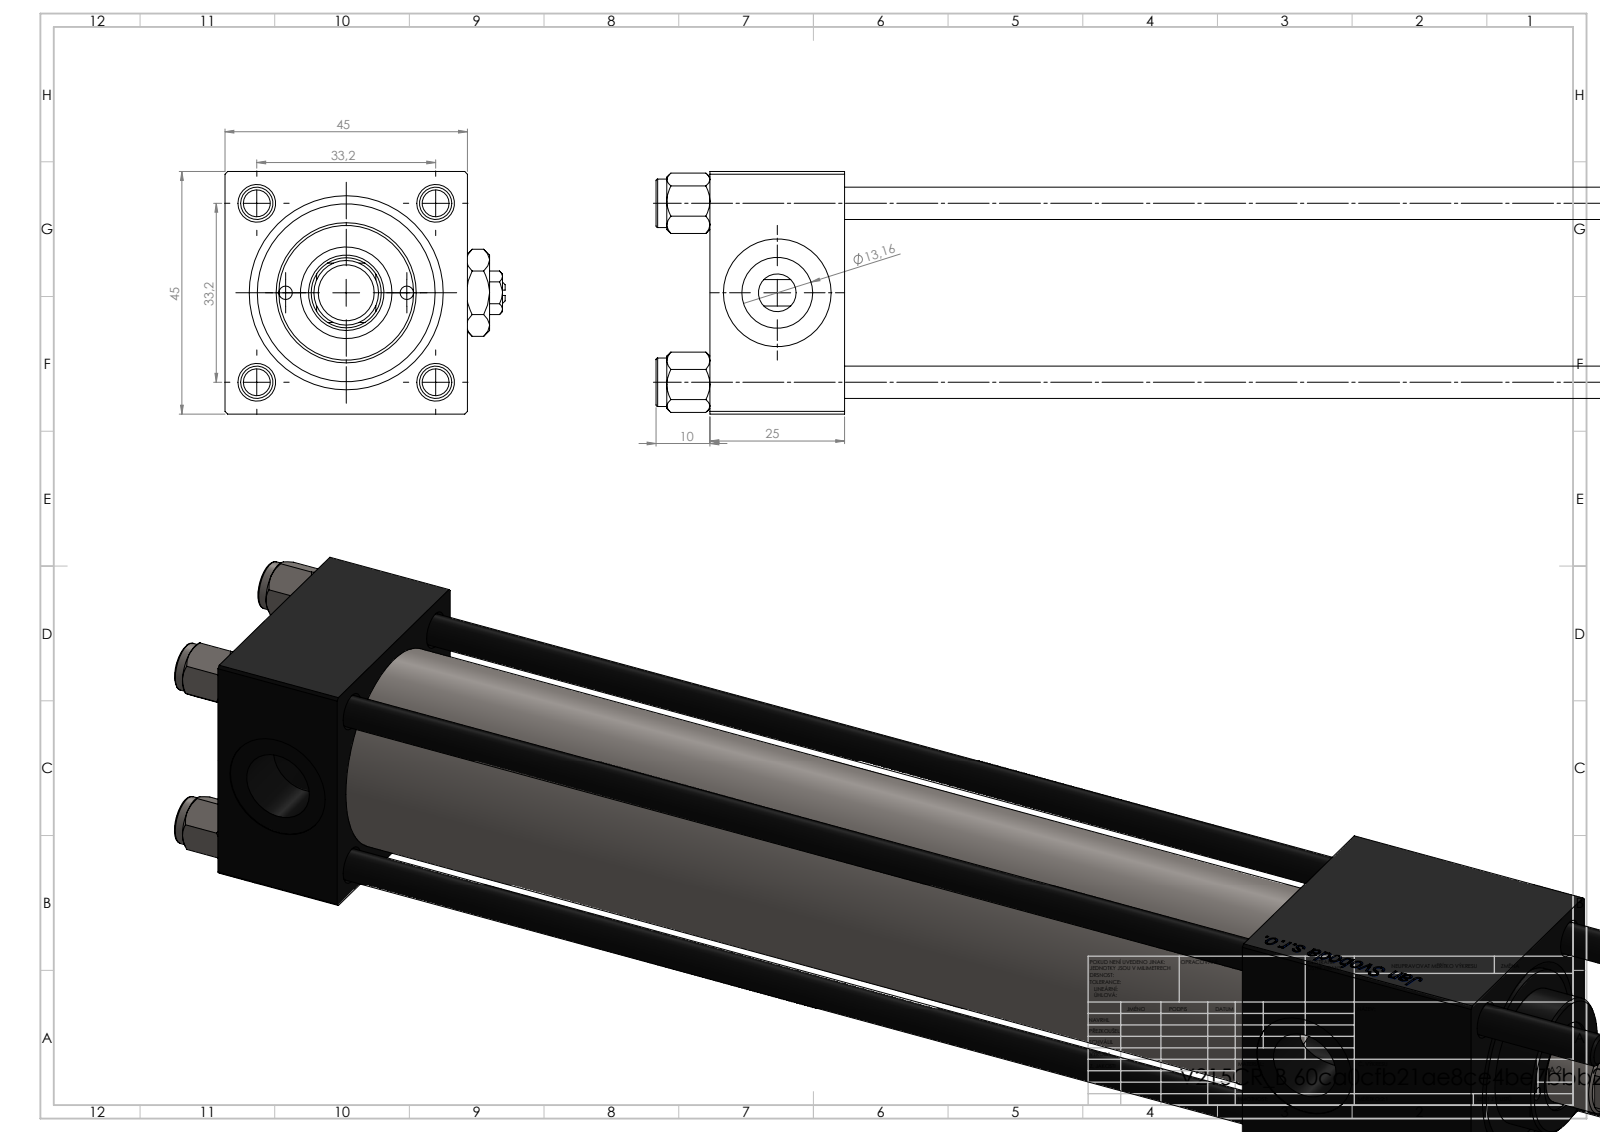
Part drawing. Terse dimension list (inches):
name: V215CR_VCP_B; V215_VC_A; ROD_END_AH; Zatka_pro_OIL_PORT (+3 more)
written by: SolidWorks 2019 (CONFIG_CONTROL_DESIGN)
unit: in
bodies: 13 solids, 1228 faces (460 planar, 92 cylindrical, 676 other)
size: 12.362 × 2.047 × 1.772
volume: 17.25 in³; area: 189.4 in²
holes: 4× ⌀0.236, 2× ⌀0.098, 2× ⌀0.276, 2× ⌀0.518, 2× ⌀0.787, 1× ⌀0.256, 1× ⌀0.551, 1× ⌀0.669, 1× ⌀0.945, 1× ⌀1.26, 1× ⌀1.299
bosses: 4× ⌀0.354, 1× ⌀1.496, 1× ⌀1.024, 1× ⌀0.472, 1× ⌀0.394
rounds: 1× R0.256
face distances: 1.772, 0.984, 10.354, 9.37, 8.465, 7.48, 1.89, 9.224, 8.24, 0.76
hole spacings: 0.687, 0.924, 1.276, 1.307, 0.443, 1.848, 0.886, 8.484
